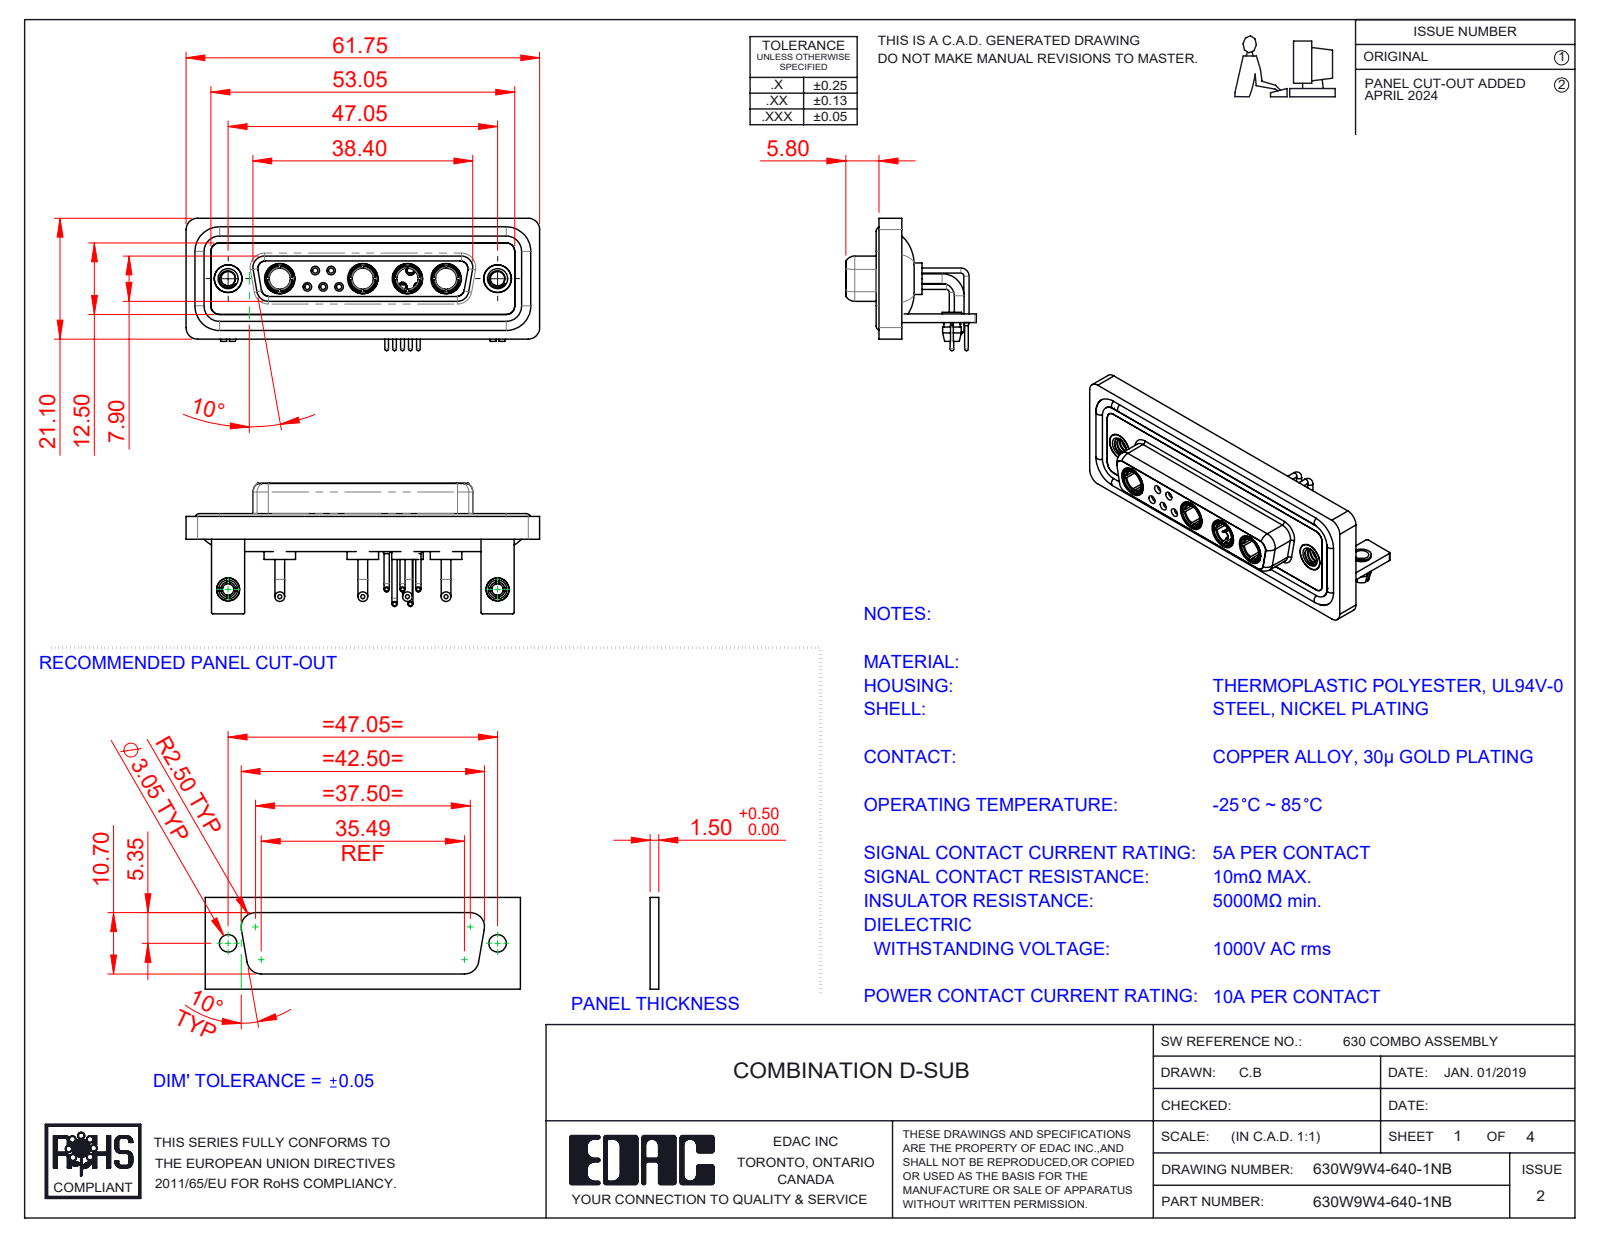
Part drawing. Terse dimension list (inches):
name: Power Socket_10A RA; 630Combo Contact Row 1_50 Contacts; 630Combo Housing_9W4; 630W9W4-640-1NB (+7 more)
written by: SolidWorks 2023 (CONFIG_CONTROL_DESIGN)
unit: in
bodies: 24 solids, 1097 faces (364 planar, 457 cylindrical, 276 other)
size: 2.431 × 0.91 × 0.898
volume: 0.526 in³; area: 22.93 in²
holes: 7× ⌀0.079, 6× ⌀0.191, 5× ⌀0.035, 5× ⌀0.043, 5× ⌀0.059, 4× ⌀0.098, 4× ⌀0.146, 4× ⌀0.209, 3× ⌀0.063, 2× ⌀0.067, 2× ⌀0.126, 2× ⌀0.157
bosses: 10× ⌀0.035, 9× ⌀0.063, 8× ⌀0.067, 5× ⌀0.079, 5× ⌀0.059, 5× ⌀0.026, 4× ⌀0.217, 4× ⌀0.205
rounds: 19× R0.079, 18× R0.059, 16× R0.01, 8× R0.053, 8× R0.063, 5× R0.02, 4× R0.024, 4× R0.026
face distances: 0.016, 0.071, 0.114, 0.059, 0.146, 0.161, 0.043, 0.055, 0.063, 0.098
hole spacings: 0.124, 0.109, 0.198, 0.545, 0.436, 0.504, 0.61, 0.218
